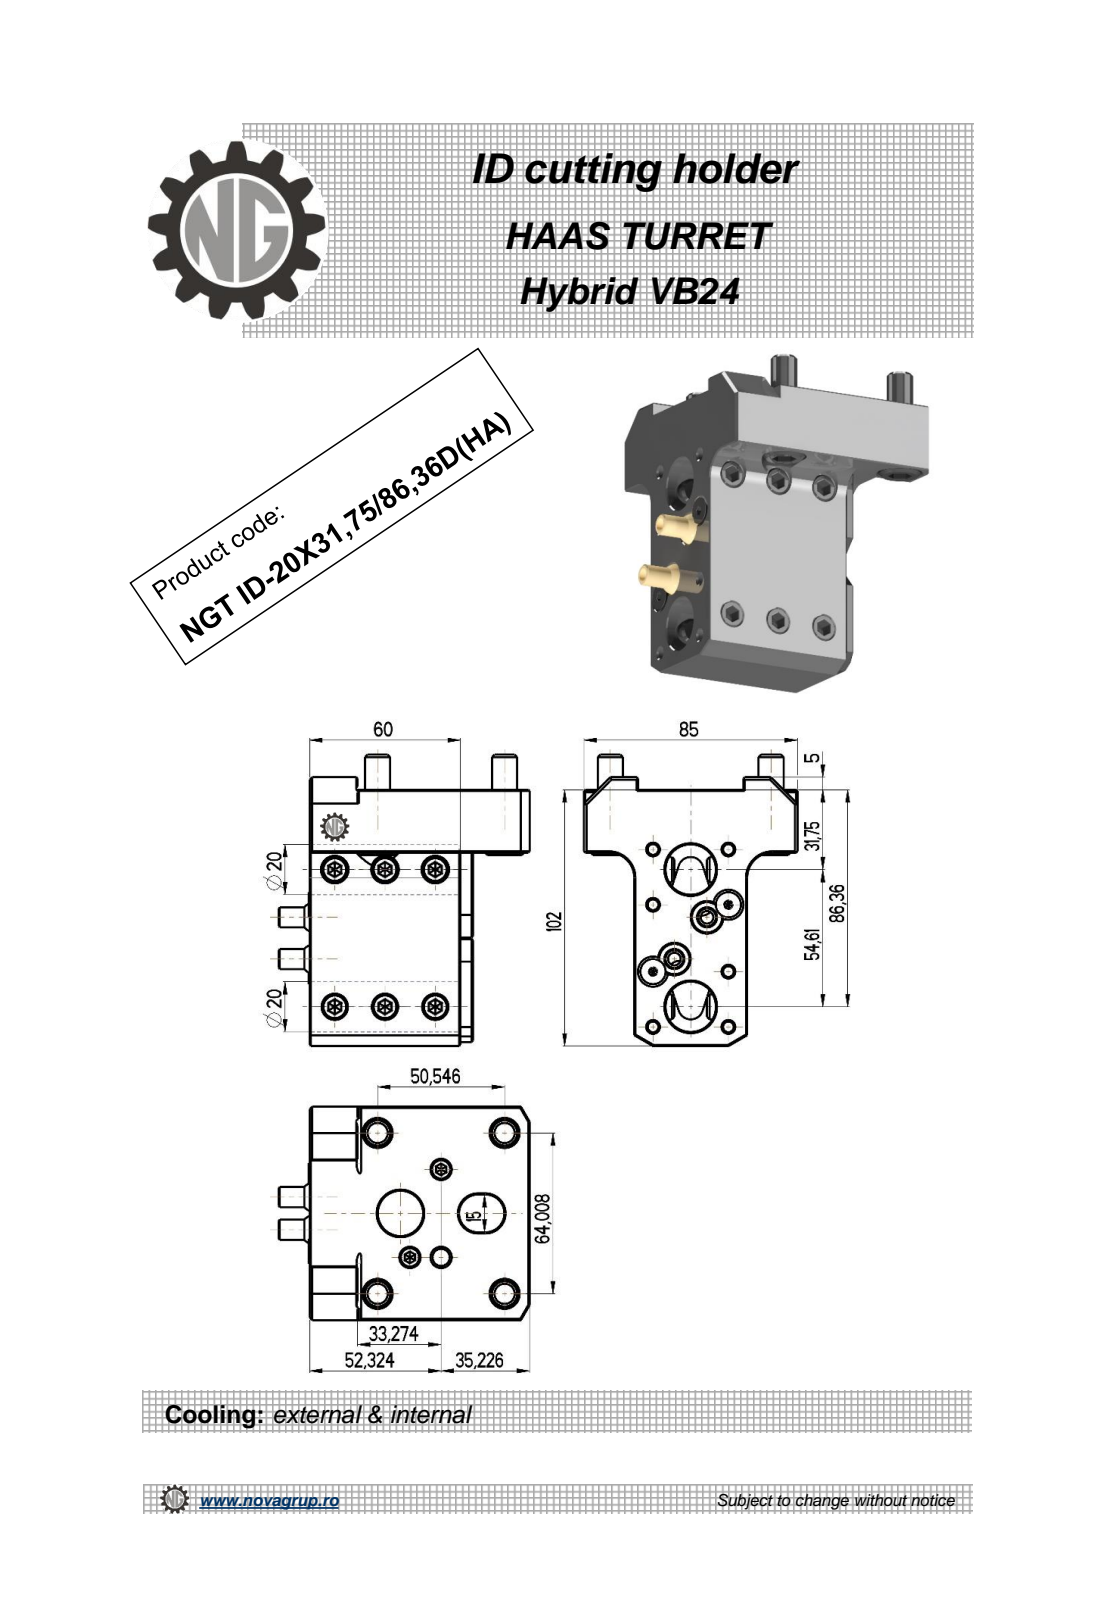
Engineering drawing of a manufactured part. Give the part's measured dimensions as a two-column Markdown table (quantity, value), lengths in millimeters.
| quantity | value |
| --- | --- |
| part name | NGT_ID_20_31_75_86_36D_HA |
| STEP written by | PRO/ENGINEER BY PARAMETRIC TECHNOLOGY CORPORATION, 2010280 (CONFIG_CONTROL_DESIGN) |
| units | millimeters |
| bodies | 1 solid, 698 faces (298 planar, 200 cylindrical, 200 other) |
| overall size | 116 × 99.89 × 85 |
| volume | 368 324 mm³ |
| surface area | 54 984 mm² |
| round holes (diameter × count) | 11 × 3, 5 × 2, 20 × 2, 6.8 × 1, 18 × 1 |
| round bosses / shafts (diameter × count) | 10 × 12, 8 × 2 |
| partial cylindrical surfaces (radius × count) | 0.51 × 60, 0.32 × 20, 0.2 × 12, 0.41 × 6, 5 × 6, 10 × 4, 7.5 × 2 |
| main face-to-face distances | 65, 20, 45, 85, 5, 102, 77, 25, 22.55, 87.55 |
| hole center spacings | 20, 20.08, 36.2, 21.09, 23.83, 40, 54.61 |
